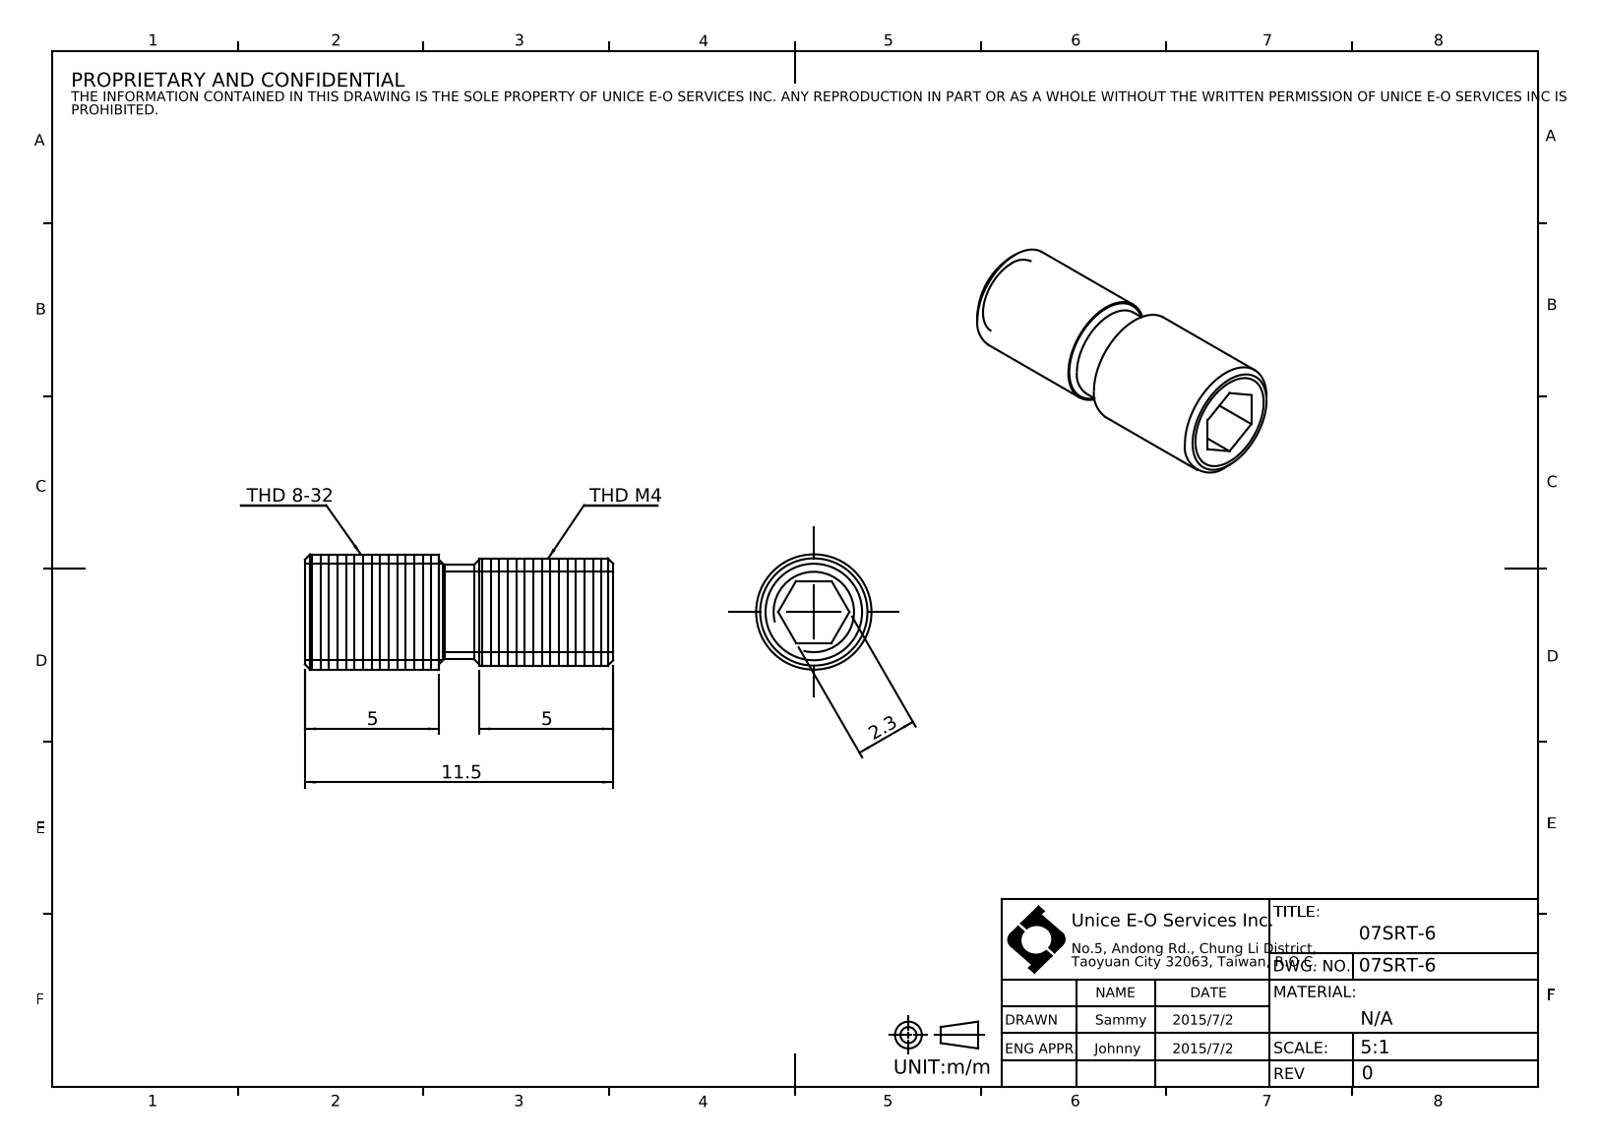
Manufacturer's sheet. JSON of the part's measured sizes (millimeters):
{"part_name": "07SRT-6", "step_written_by": "SolidWorks 2016 (CONFIG_CONTROL_DESIGN)", "units": "millimeters", "bodies": {"solids": 1, "faces": 32, "planar": 18, "cylindrical": 6, "other": 8}, "overall_size": [11.5, 4.3, 4.3], "volume_mm3": 122, "surface_area_mm2": 224, "round_bosses_or_shafts": [[4.3, 1], [4, 1], [3.5, 1]], "face_to_face_distances": [2.3, 3, 8.5, 11.5, 5.5, 5, 6.5, 2, 3.5, 1.5]}
